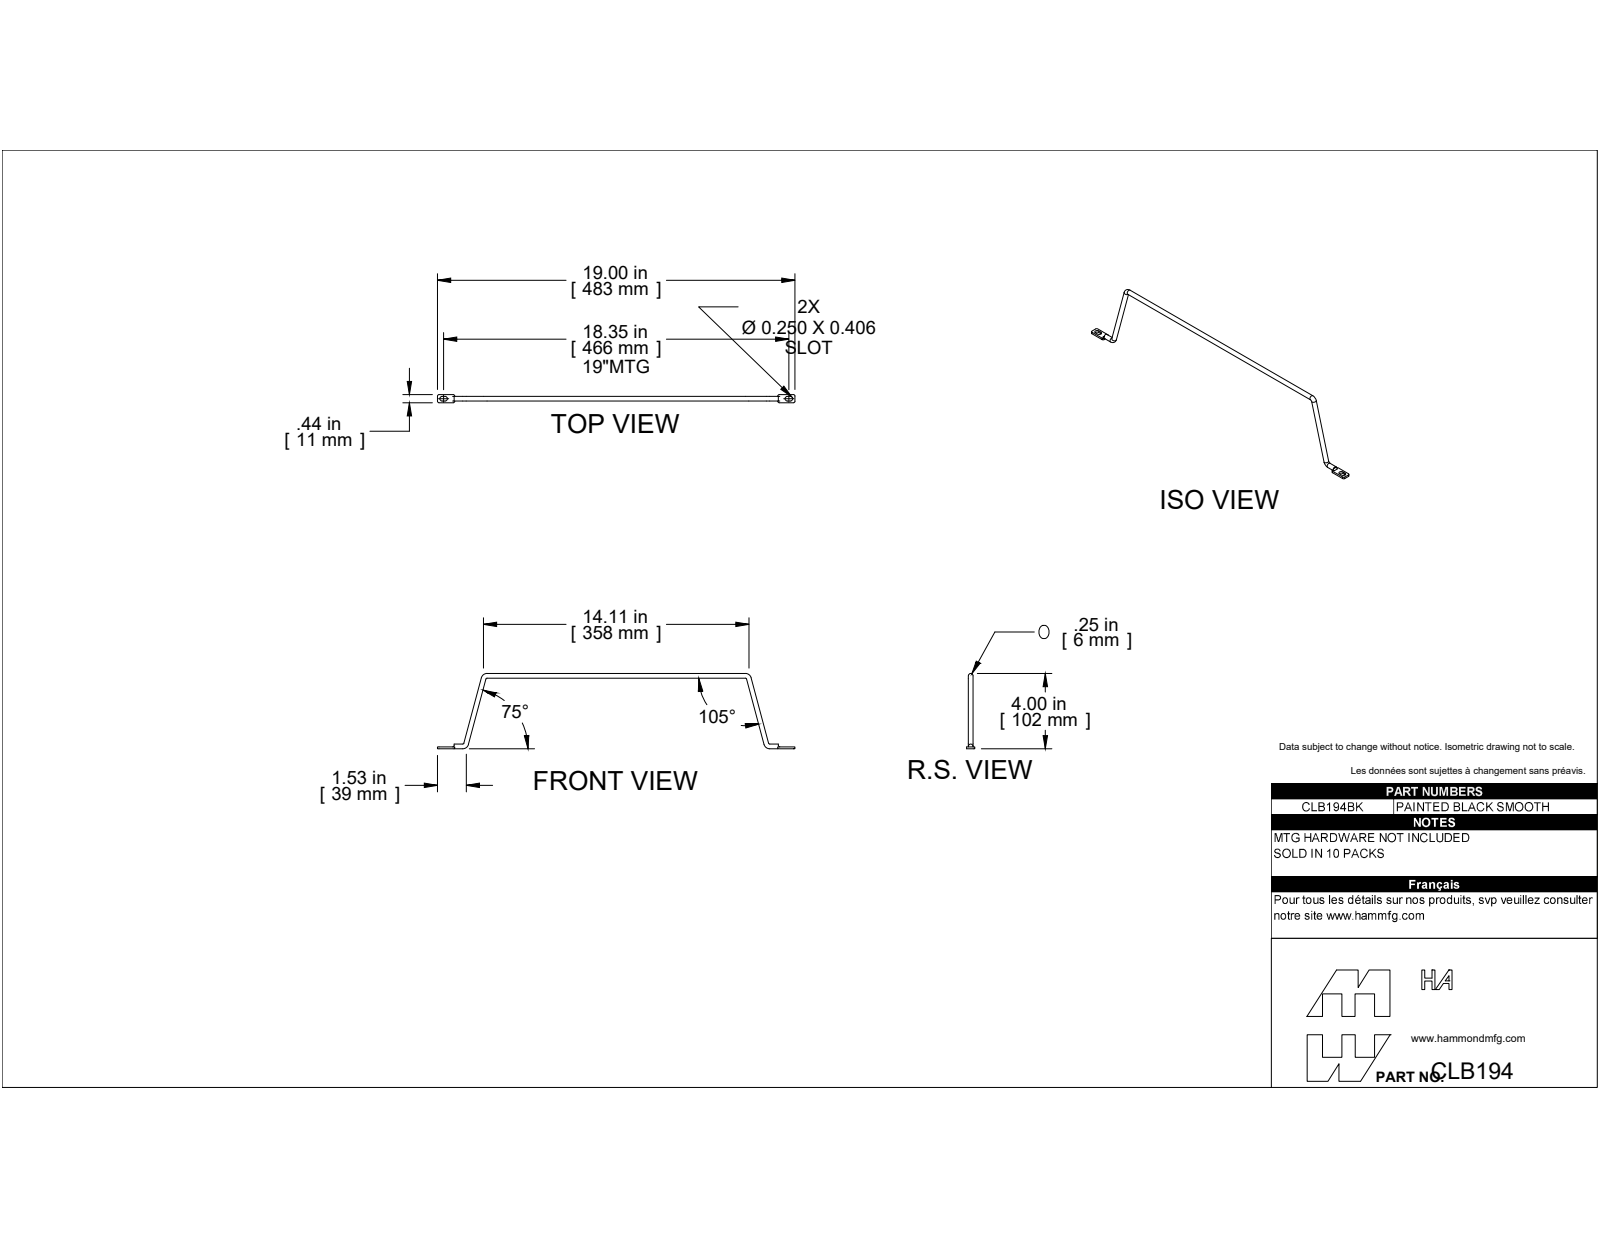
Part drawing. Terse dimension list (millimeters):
written by: Unknown (AUTOMOTIVE_DESIGN)
unit: mm
bodies: 1 solid, 43 faces (20 planar, 19 cylindrical, 4 other)
size: 482.6 × 101.6 × 11.05
volume: 19 268 mm³; area: 12 769 mm²
bosses: 4× ⌀6.35
rounds: 10× R2.03, 4× R3.17
face distances: 2.53, 11.04, 2.35, 8.69, 6.34, 482.6, 22.48, 460.12, 23.27, 459.33
